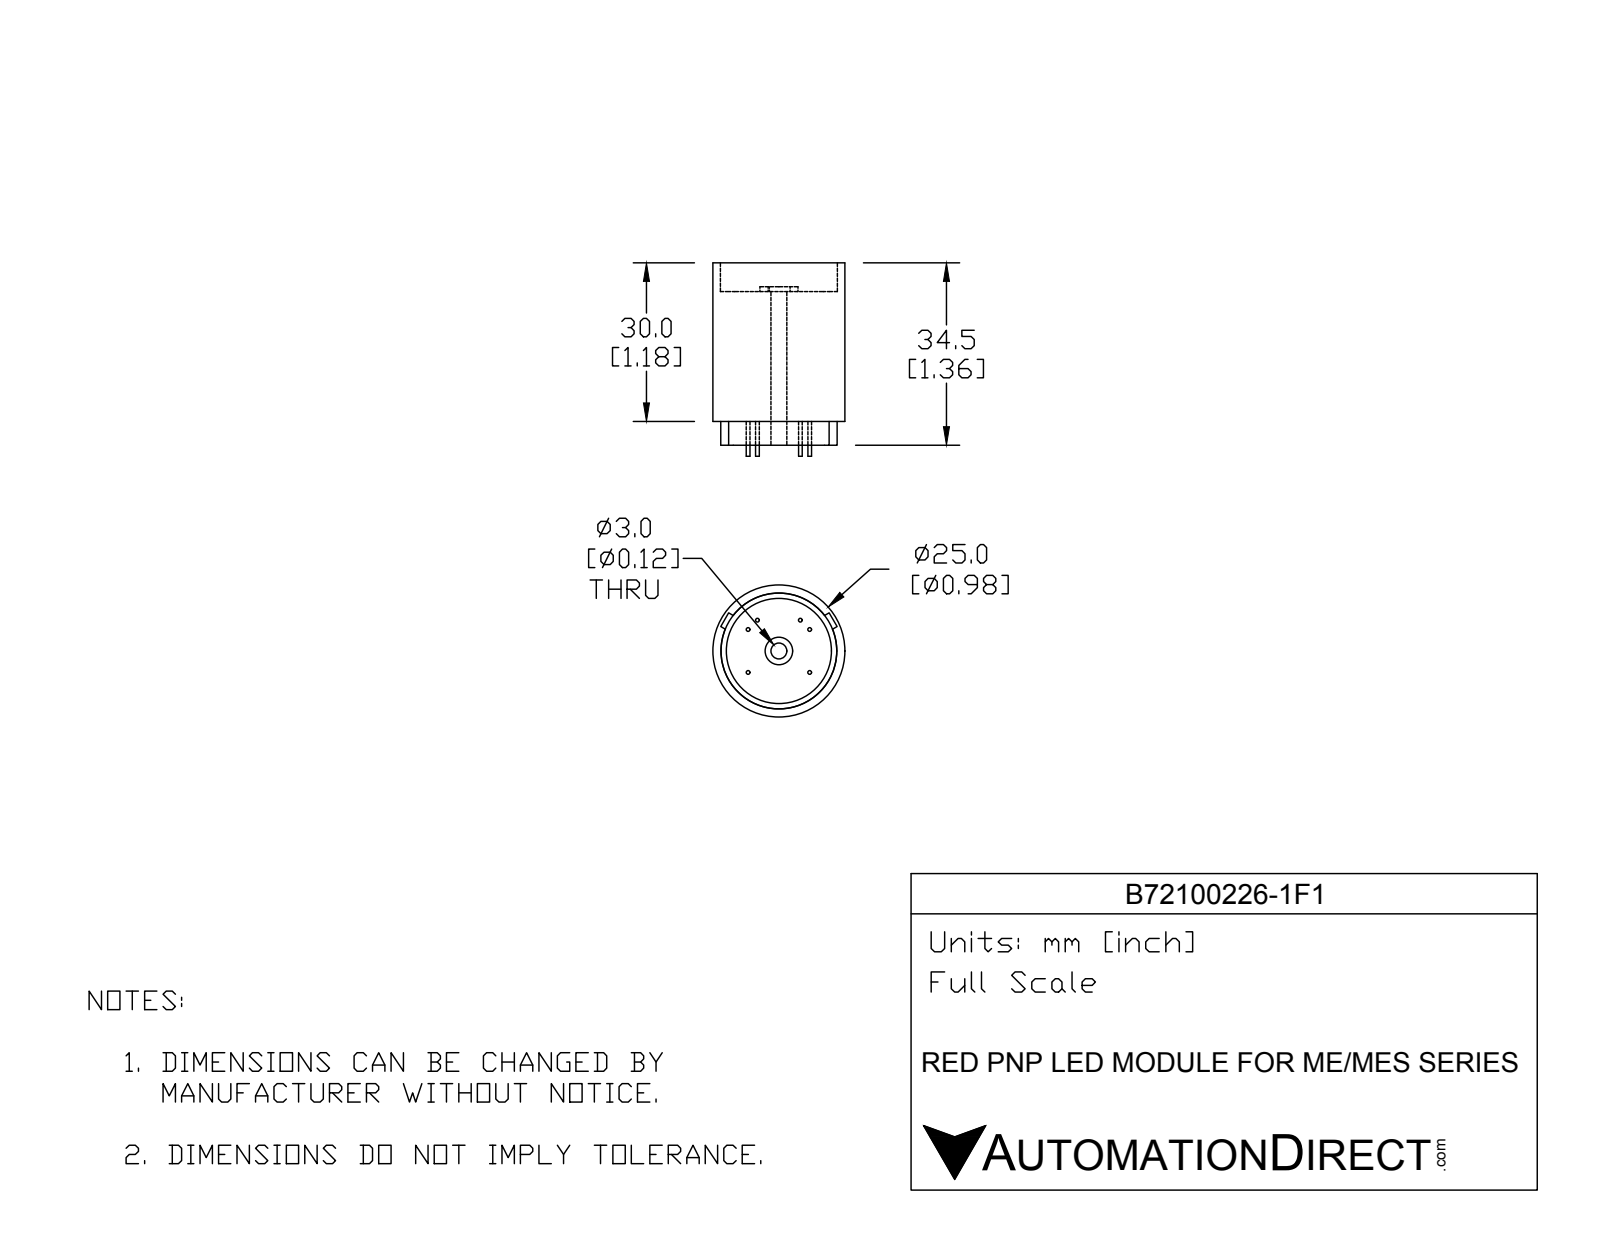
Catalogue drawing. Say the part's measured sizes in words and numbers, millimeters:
The part is named "B72100226-1F1". Its 3-D file was written by "SolidWorks 2016 (AUTOMOTIVE_DESIGN)". It is 9 solids with 69 faces: 36 planar, 33 cylindrical and 0 other. Overall it measures 36.6 by 25 by 25 millimeters. Its volume is 12 963 cubic millimeters and its surface area 4 884 square millimeters. Round holes: 1 of diameter 3, 1 of diameter 4.22, 1 of diameter 19.9, 1 of diameter 21.5. Round bosses or shafts: 6 of diameter 0.7, 1 of diameter 25, 1 of diameter 21.9, 1 of diameter 7.22, 1 of diameter 5.2. The main face-to-face distances are 24.56, 30, 5.44, 4.5, 29.06, 34.5, 25.5, 0.94, 3.05, 3.1.
